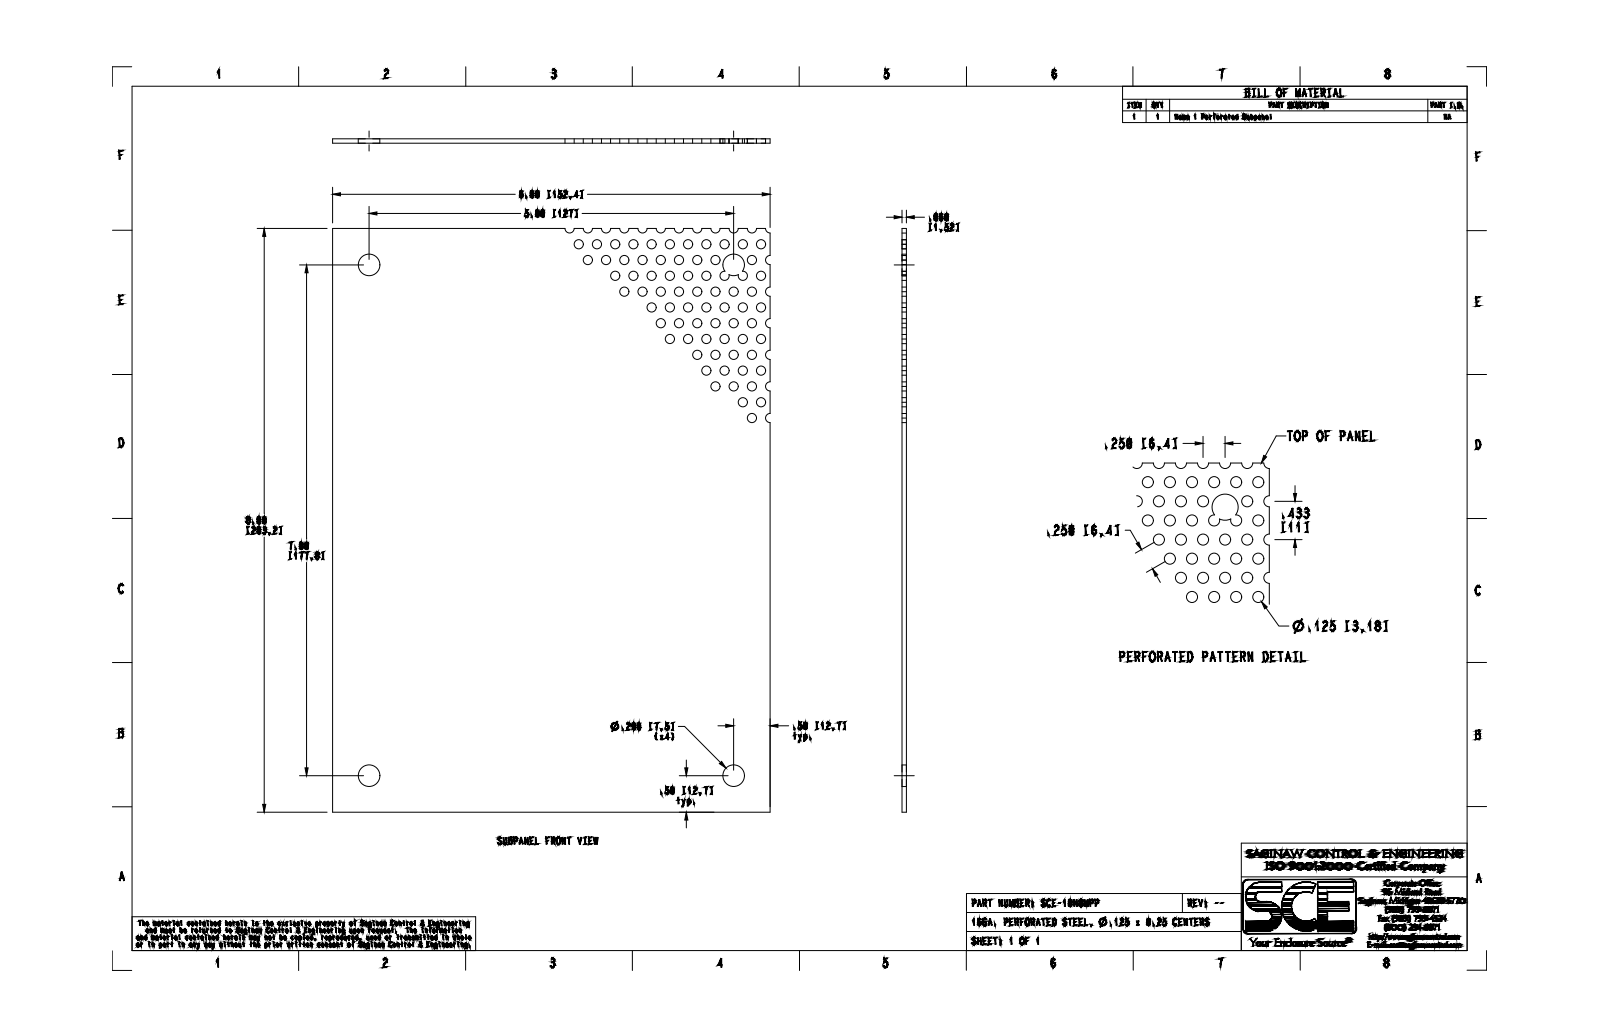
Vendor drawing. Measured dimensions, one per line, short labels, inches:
name: SCE-10N8MPP
written by: SolidWorks 2019 (CONFIG_CONTROL_DESIGN)
unit: in
bodies: 1 solid, 116 faces (23 planar, 93 cylindrical, 0 other)
size: 8 × 6 × 0.06
volume: 2.806 in³; area: 97.13 in²
holes: 46× ⌀0.125, 24× ⌀0.125, 4× ⌀0.296
rounds: 11× R0.063, 7× R0.062
face distances: 0.06, 6, 8
hole spacings: 0.25, 0.661, 0.5, 0.433, 0.433, 1.323, 1.09, 0.901
